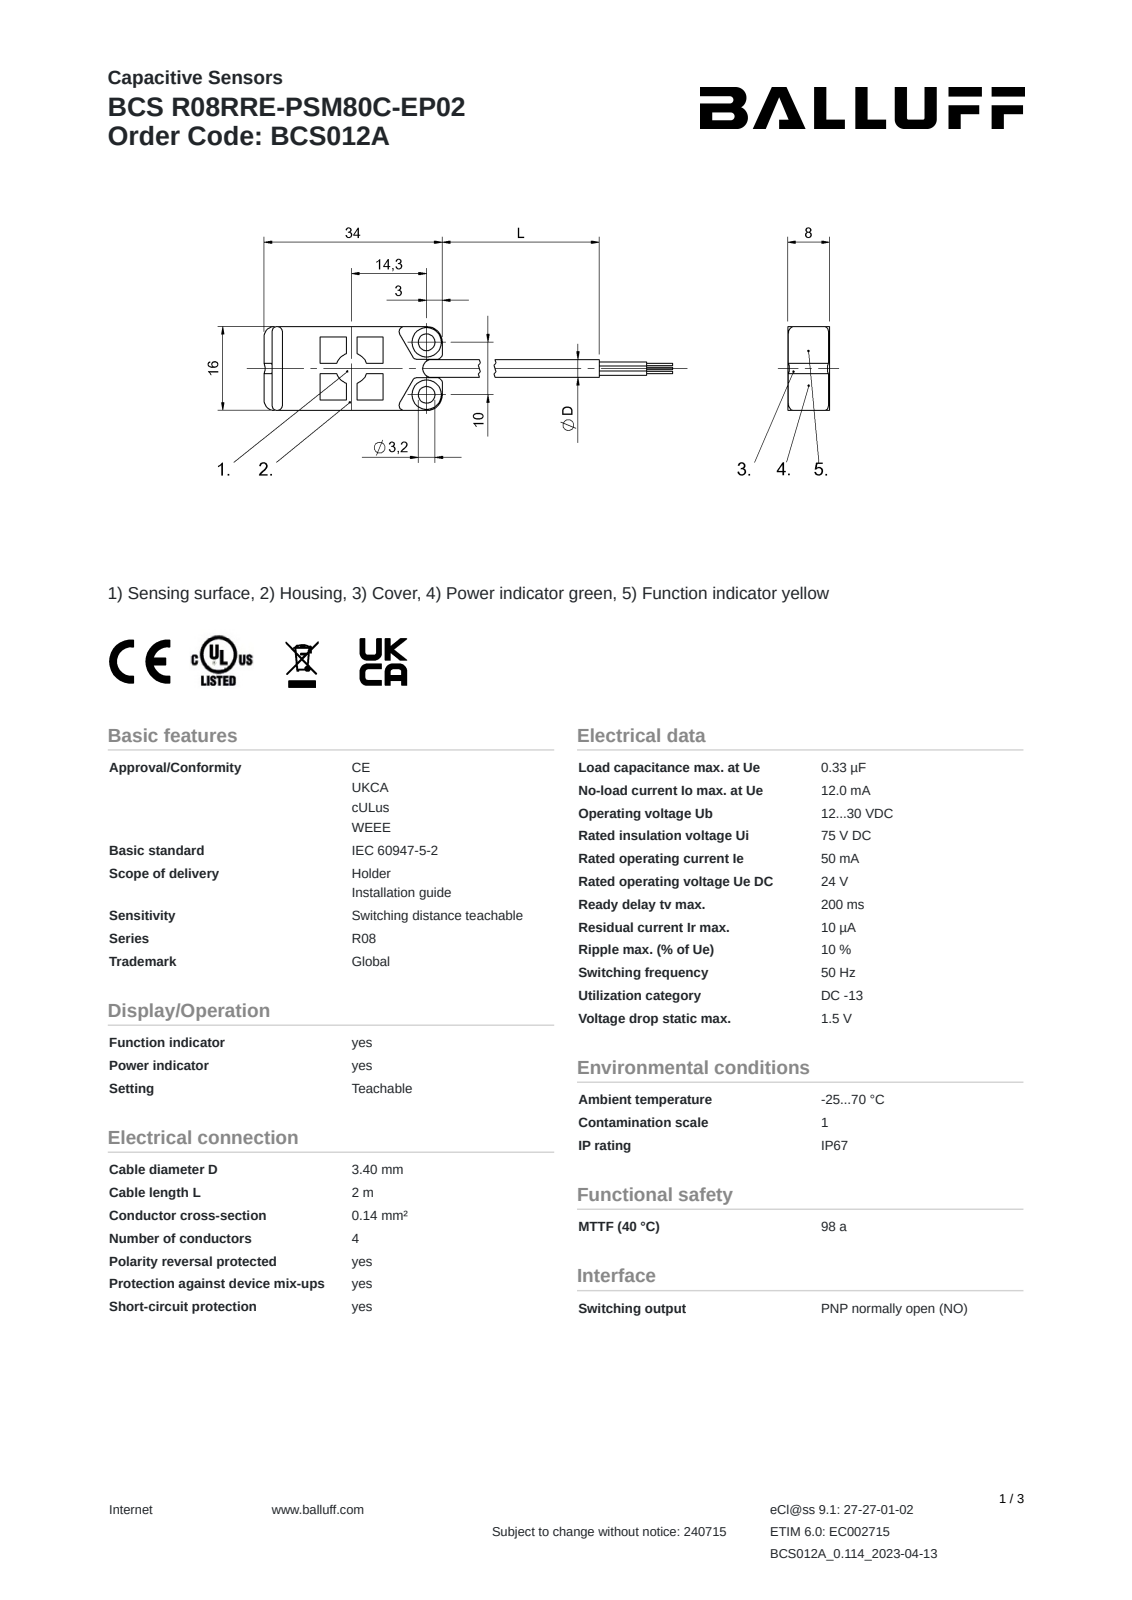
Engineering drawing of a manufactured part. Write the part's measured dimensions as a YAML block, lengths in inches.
part_name: "BCS012A"
step_written_by: "SolidWorks 2021 (AUTOMOTIVE_DESIGN)"
units: inches
bodies: {solids: 2, faces: 654, planar: 453, cylindrical: 176, other: 25}
overall_size: [2.953, 2.146, 0.37]
volume: 0.598
surface_area: 12.73
round_holes:
  - {diameter: 0.126, count: 6}
  - {diameter: 0.087, count: 1}
round_bosses_or_shafts:
  - {diameter: 0.079, count: 2}
  - {diameter: 0.134, count: 1}
  - {diameter: 0.106, count: 1}
partial_cylinders:
  - {radius: 0.039, count: 22}
  - {radius: 0.031, count: 16}
  - {radius: 0.079, count: 14}
  - {radius: 0.016, count: 8}
  - {radius: 0.02, count: 4}
  - {radius: 0.033, count: 4}
  - {radius: 0.059, count: 3}
  - {radius: 0.118, count: 3}
face_to_face_distances: [0.15, 0.039, 0.118, 0.157, 0.307, 0.634, 0.031, 0.268, 0.059, 0.299]
hole_center_spacings: [0.4, 0.837, 1.163, 1.168, 1.526, 2.053, 0.394, 0.567]
